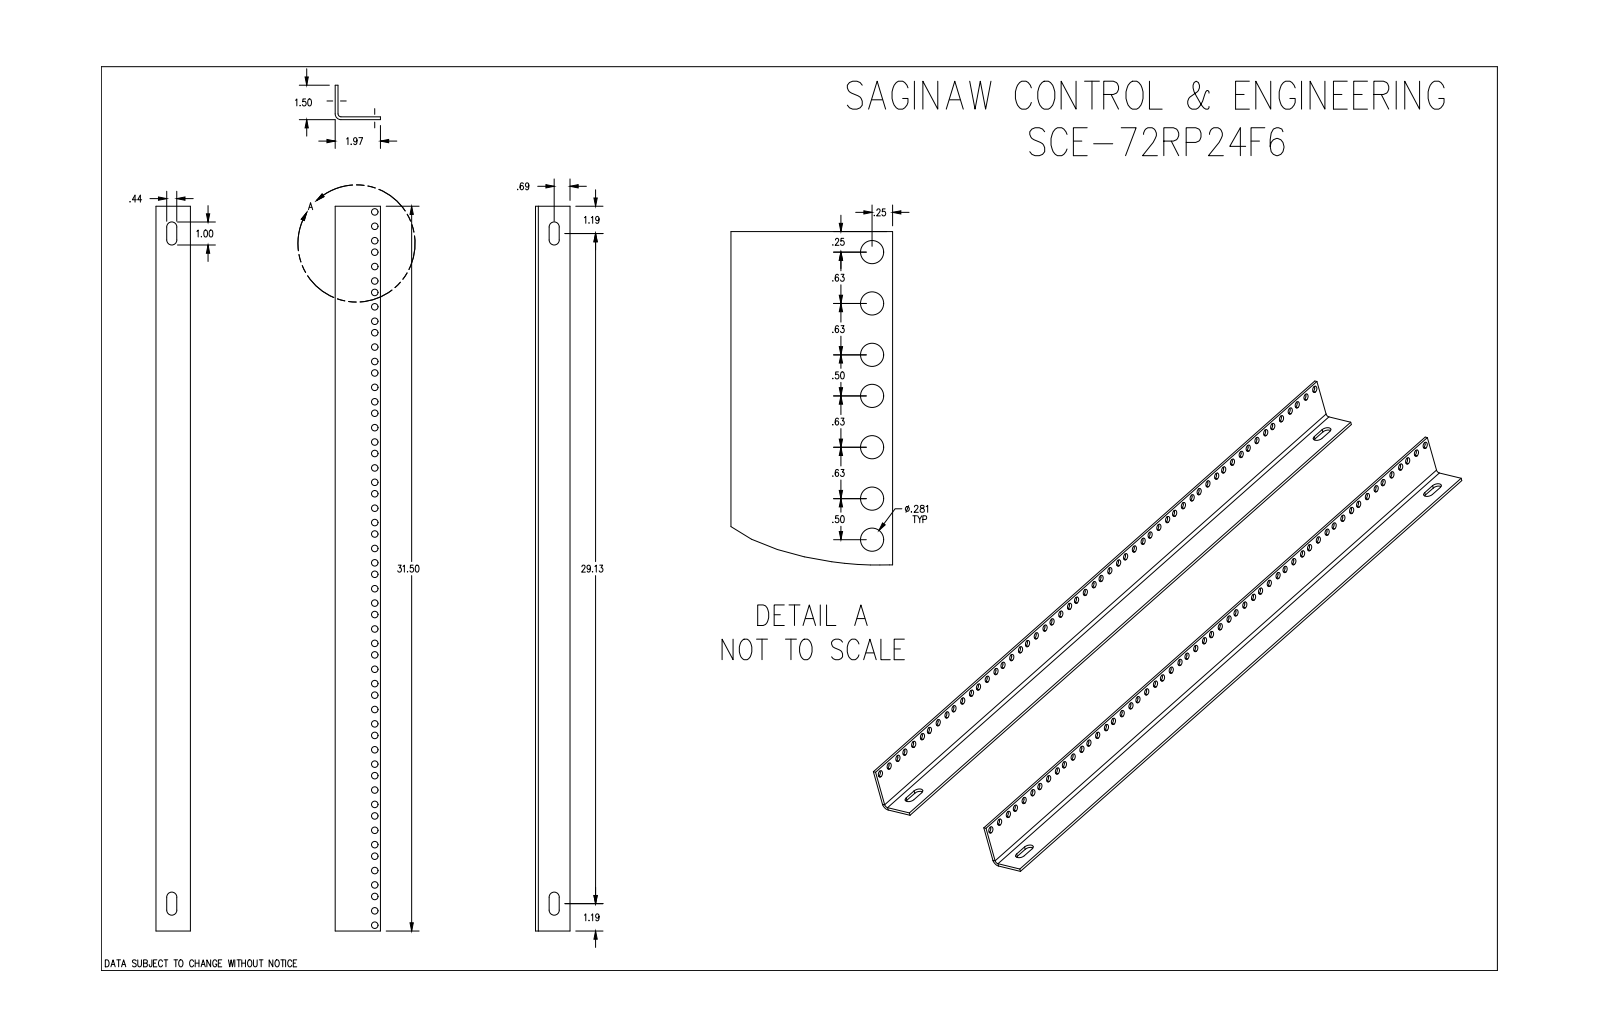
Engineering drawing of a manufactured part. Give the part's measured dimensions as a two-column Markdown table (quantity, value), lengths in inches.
| quantity | value |
| --- | --- |
| part name | SCE-72RP24F6 |
| STEP written by | SolidWorks 2019 (CONFIG_CONTROL_DESIGN) |
| units | inches |
| bodies | 1 solid, 130 faces (16 planar, 114 cylindrical, 0 other) |
| overall size | 31.5 × 1.969 × 1.5 |
| volume | 12.33 in³ |
| surface area | 212.6 in² |
| round holes (diameter × count) | 0.281 × 54 |
| partial cylindrical surfaces (radius × count) | 0.219 × 4, 0.125 × 1, 0.25 × 1 |
| main face-to-face distances | 0.125, 1.969, 1.844, 1.5, 1.375, 31.5, 0.594, 1.031, 0.469, 0.906 |
| hole center spacings | 1.75, 3.5, 5.25, 7, 8.75, 0.625, 0.625, 1.25 |
